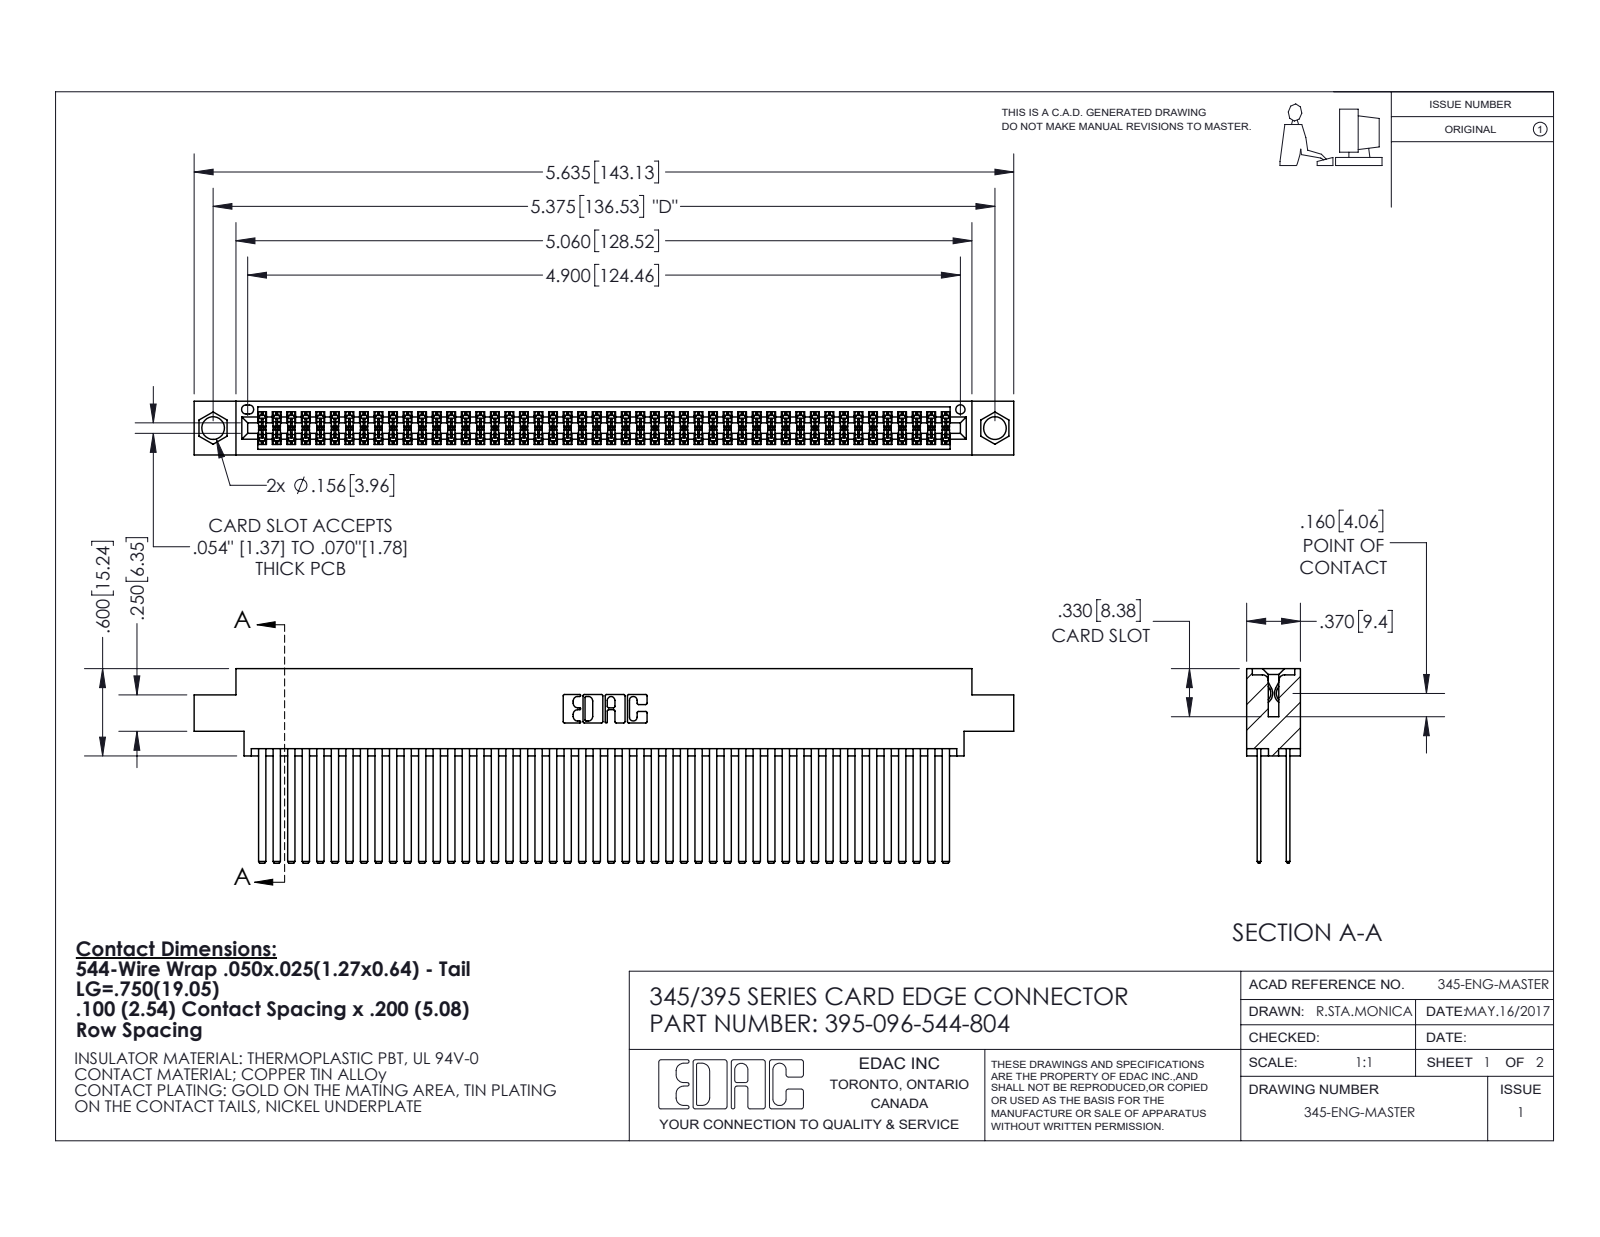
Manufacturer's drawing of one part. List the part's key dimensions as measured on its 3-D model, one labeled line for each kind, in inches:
Part name (STEP PRODUCT): 345 Part_0.170 Offset - 0.156 Dia-TI; 345-292-001_345-293-144; 395-096-544-804
STEP written by: SolidWorks 2020 (CONFIG_CONTROL_DESIGN)
Units: inches
Bodies: 97 solids, 4368 faces (2882 planar, 1486 cylindrical, 0 other)
Overall size (bounding box): 5.635 × 1.337 × 0.37
Volume: 0.921 in³ · Surface area: 40.85 in²
Round holes (diameter × count): ⌀0.156 ×2, ⌀0.064 ×1
Partial cylindrical surfaces — rounded edges, fillets, slot ends (radius × count): R0.006 ×144, R0.01 ×22, R0.007 ×6, R0.031 ×6, R0.026 ×3, R0.014 ×2, R0.019 ×2, R0.022 ×2
Main face-to-face distances: 0.2, 0.025, 0.072, 0.098, 0.272, 0.298, 0.225, 0.175, 0.37, 0.15
Hole centre spacings: 0.27, 5.139, 5.375
